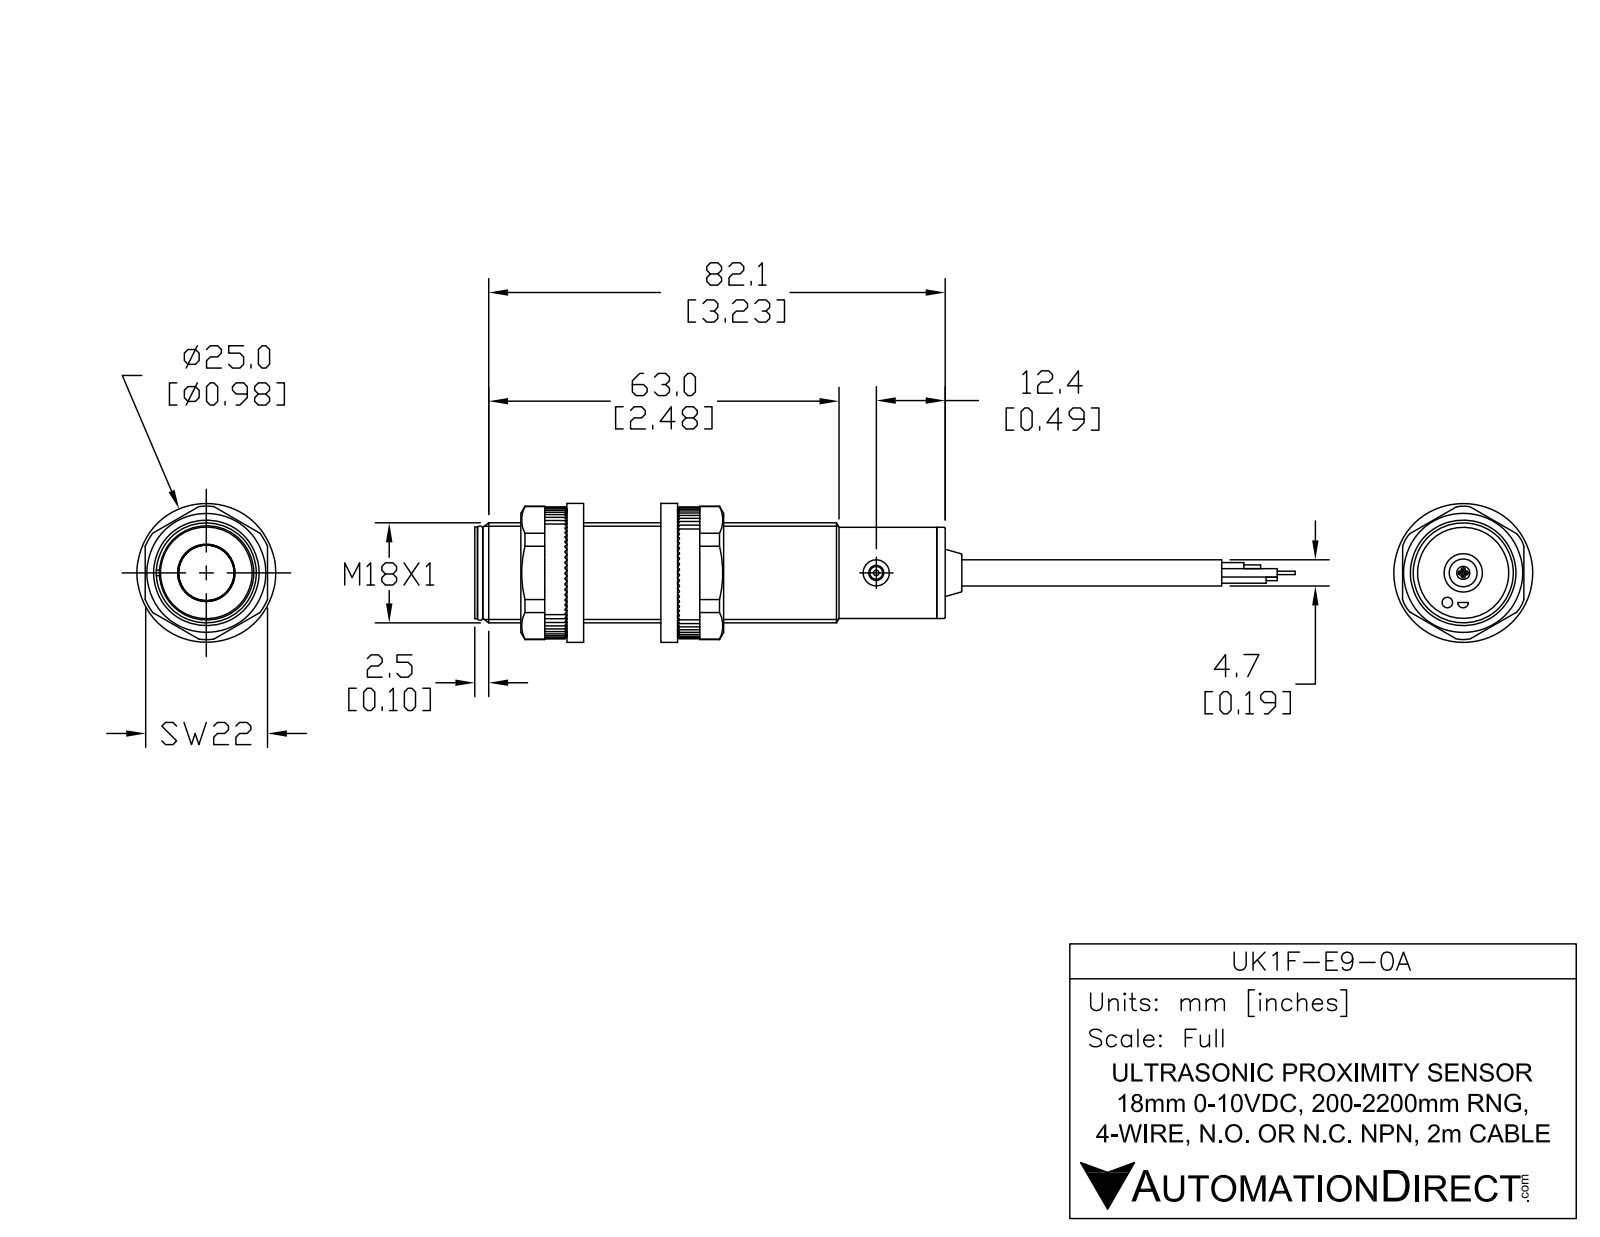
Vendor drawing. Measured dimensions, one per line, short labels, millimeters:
name: UK1F-E9-0A
written by: SolidWorks 2017 (AUTOMOTIVE_DESIGN)
unit: mm
bodies: 6 solids, 55 faces (17 planar, 24 cylindrical, 14 other)
size: 122.7 × 18 × 18
volume: 21 060 mm³; area: 6 897 mm²
holes: 2× ⌀4.7, 1× ⌀2.7
bosses: 1× ⌀18, 1× ⌀16.4, 1× ⌀15.8, 1× ⌀9.5, 1× ⌀4.8, 1× ⌀2.3
face distances: 81.1, 82.6, 1.5, 1, 82.1, 83.6, 1, 82.1, 83.6, 82.7
